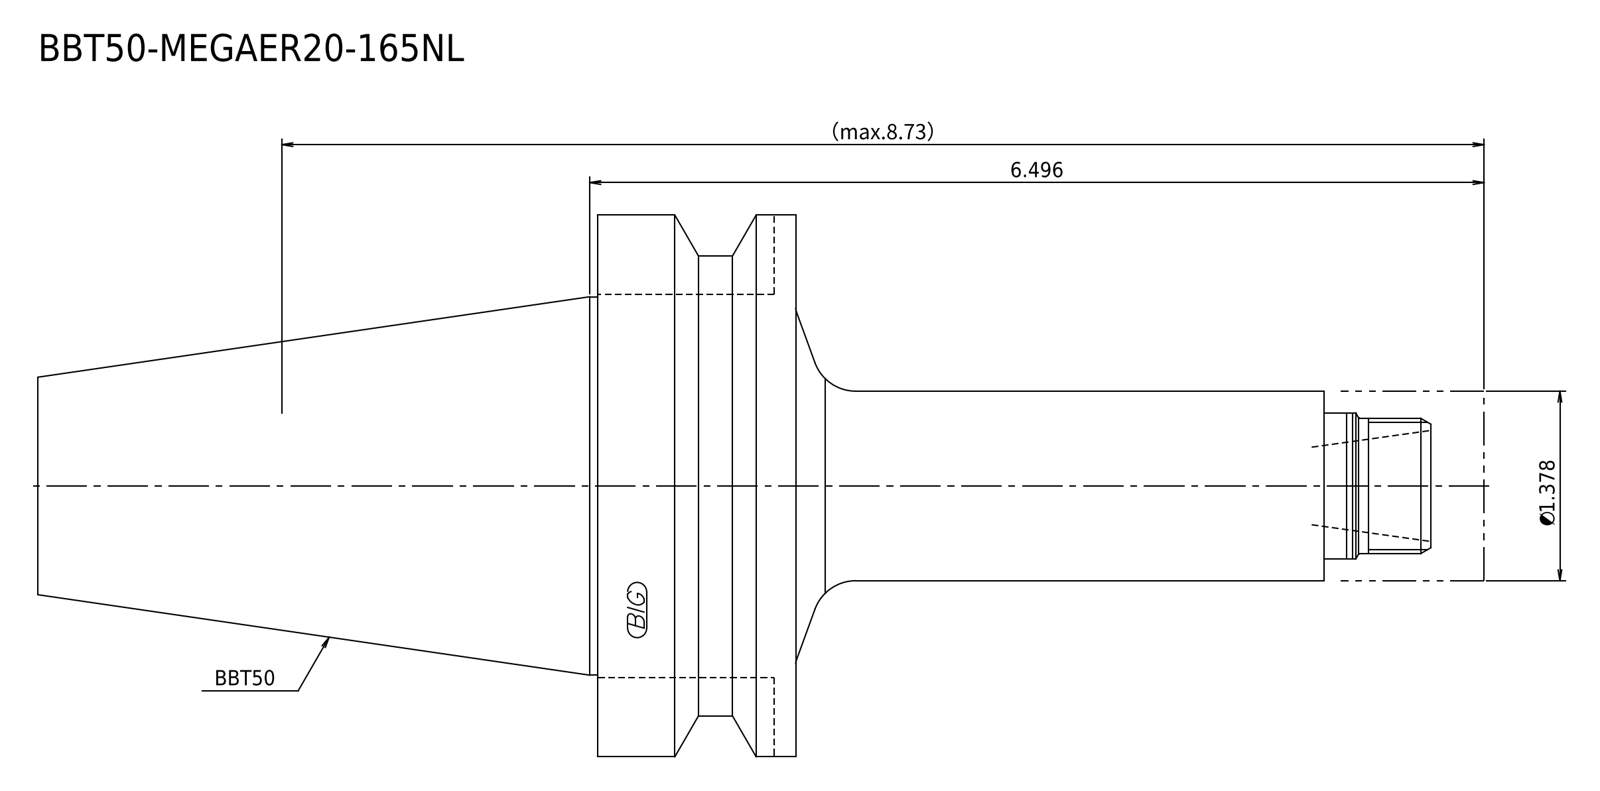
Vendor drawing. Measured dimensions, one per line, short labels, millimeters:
written by: Kubotek KeyCreator 2011 V10.0.2 (22737) (automotive_design)
unit: mm
bodies: 2 solids, 21 faces (7 planar, 8 cylindrical, 6 other)
size: 266.8 × 100 × 100
volume: 658 151 mm³; area: 61 121 mm²
bosses: 1× ⌀100, 1× ⌀85, 1× ⌀69.85, 1× ⌀35, 1× ⌀27, 1× ⌀25
face distances: 36.5, 139.8, 103.3, 100.5, 137, 240.3, 26.5, 127, 163.5, 266.8
